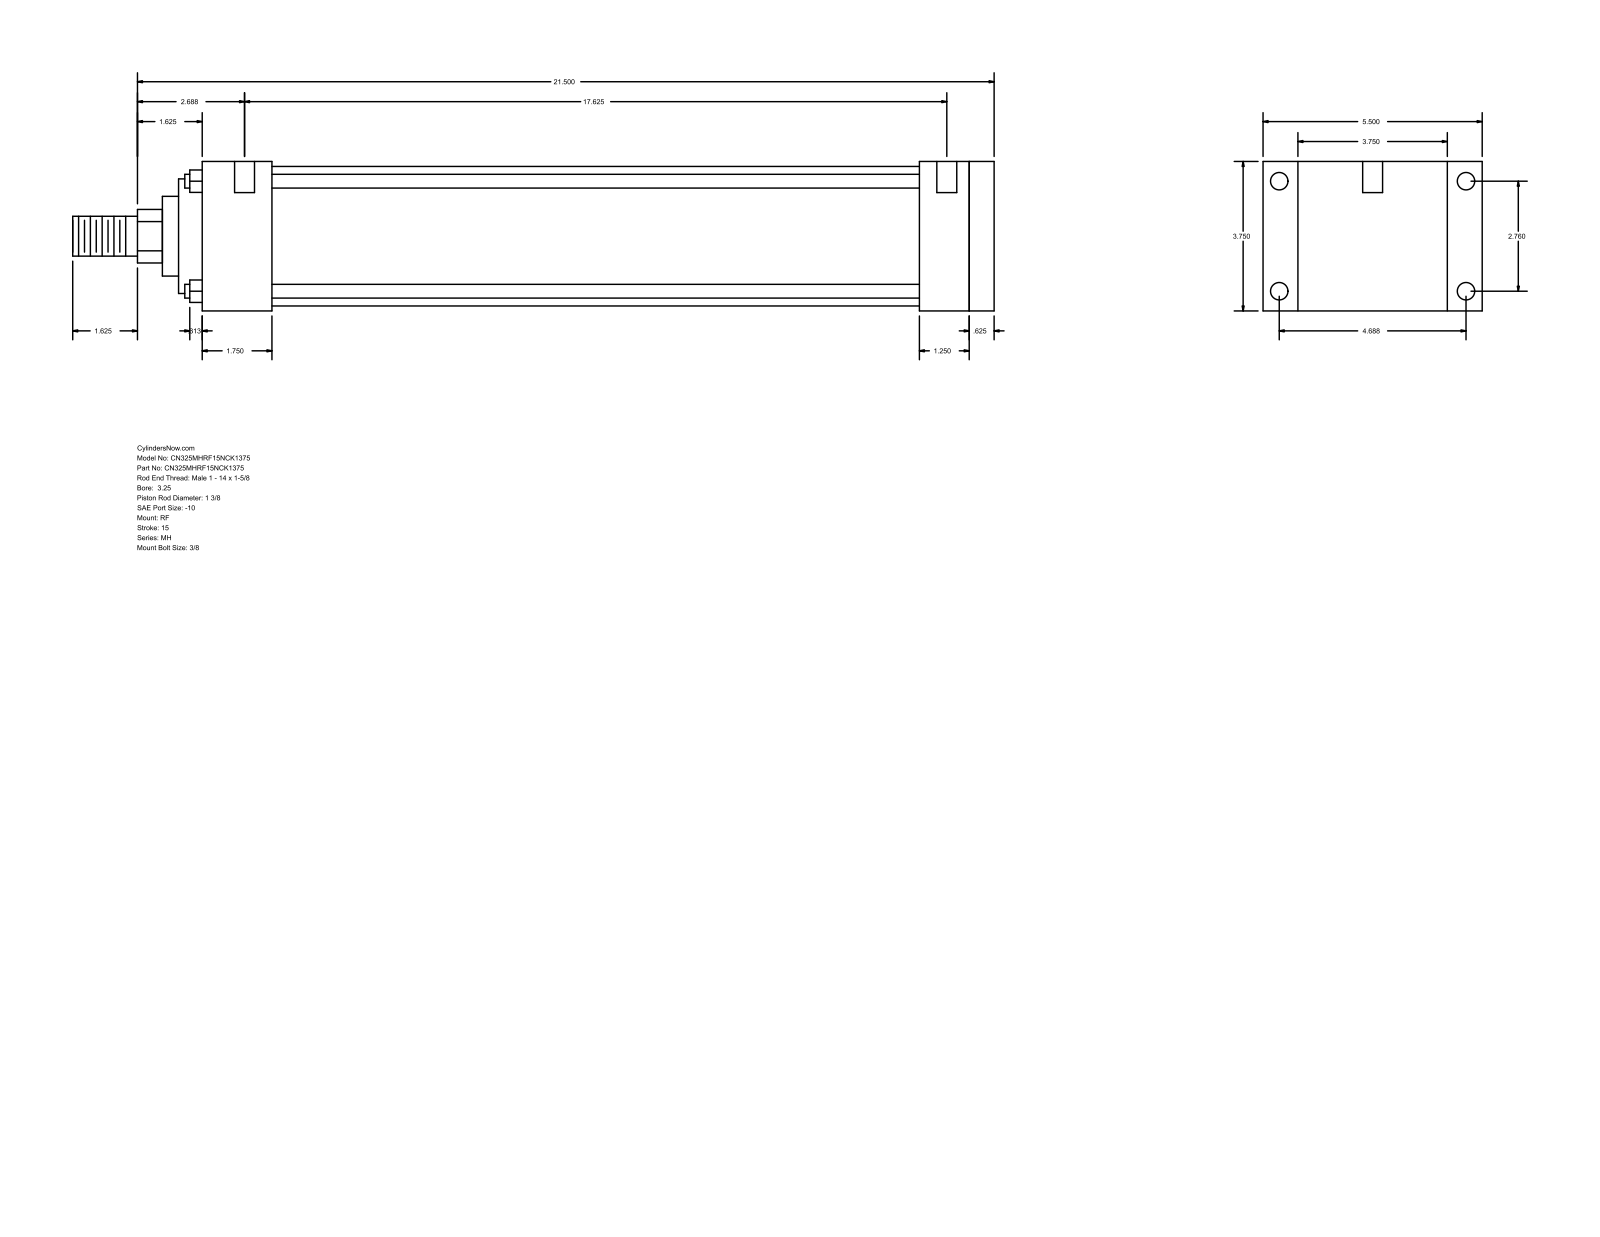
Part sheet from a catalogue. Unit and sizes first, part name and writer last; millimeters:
Units: millimetres
Overall size (bounding box): 587.38 × 139.7 × 95.25
Round holes (diameter × count): ⌀5.56 ×4, ⌀11.13 ×4, ⌀12.7 ×2
Round bosses / shafts (diameter × count): ⌀8.76 ×4, ⌀88.9 ×1, ⌀73.03 ×1, ⌀50.8 ×1, ⌀34.92 ×1, ⌀25.4 ×1
Partial cylindrical surfaces — rounded edges, fillets, slot ends (radius × count): R17.06 ×1
Main face-to-face distances: 95.24, 504.83, 488.96, 15.87, 22.23, 117.47, 44.45, 444.51, 460.38, 457.21
Hole centre spacings: 70.1, 119.06, 138.16, 454.03, 1.59, 4.76, 447.68, 449.27
Bodies: 0 solids, 94 faces (65 planar, 29 cylindrical, 0 other)
Part name (STEP PRODUCT): MH_RF__0325_1.375
STEP written by: GSSL Pune (CONFIG_CONTROL_DESIGN)
